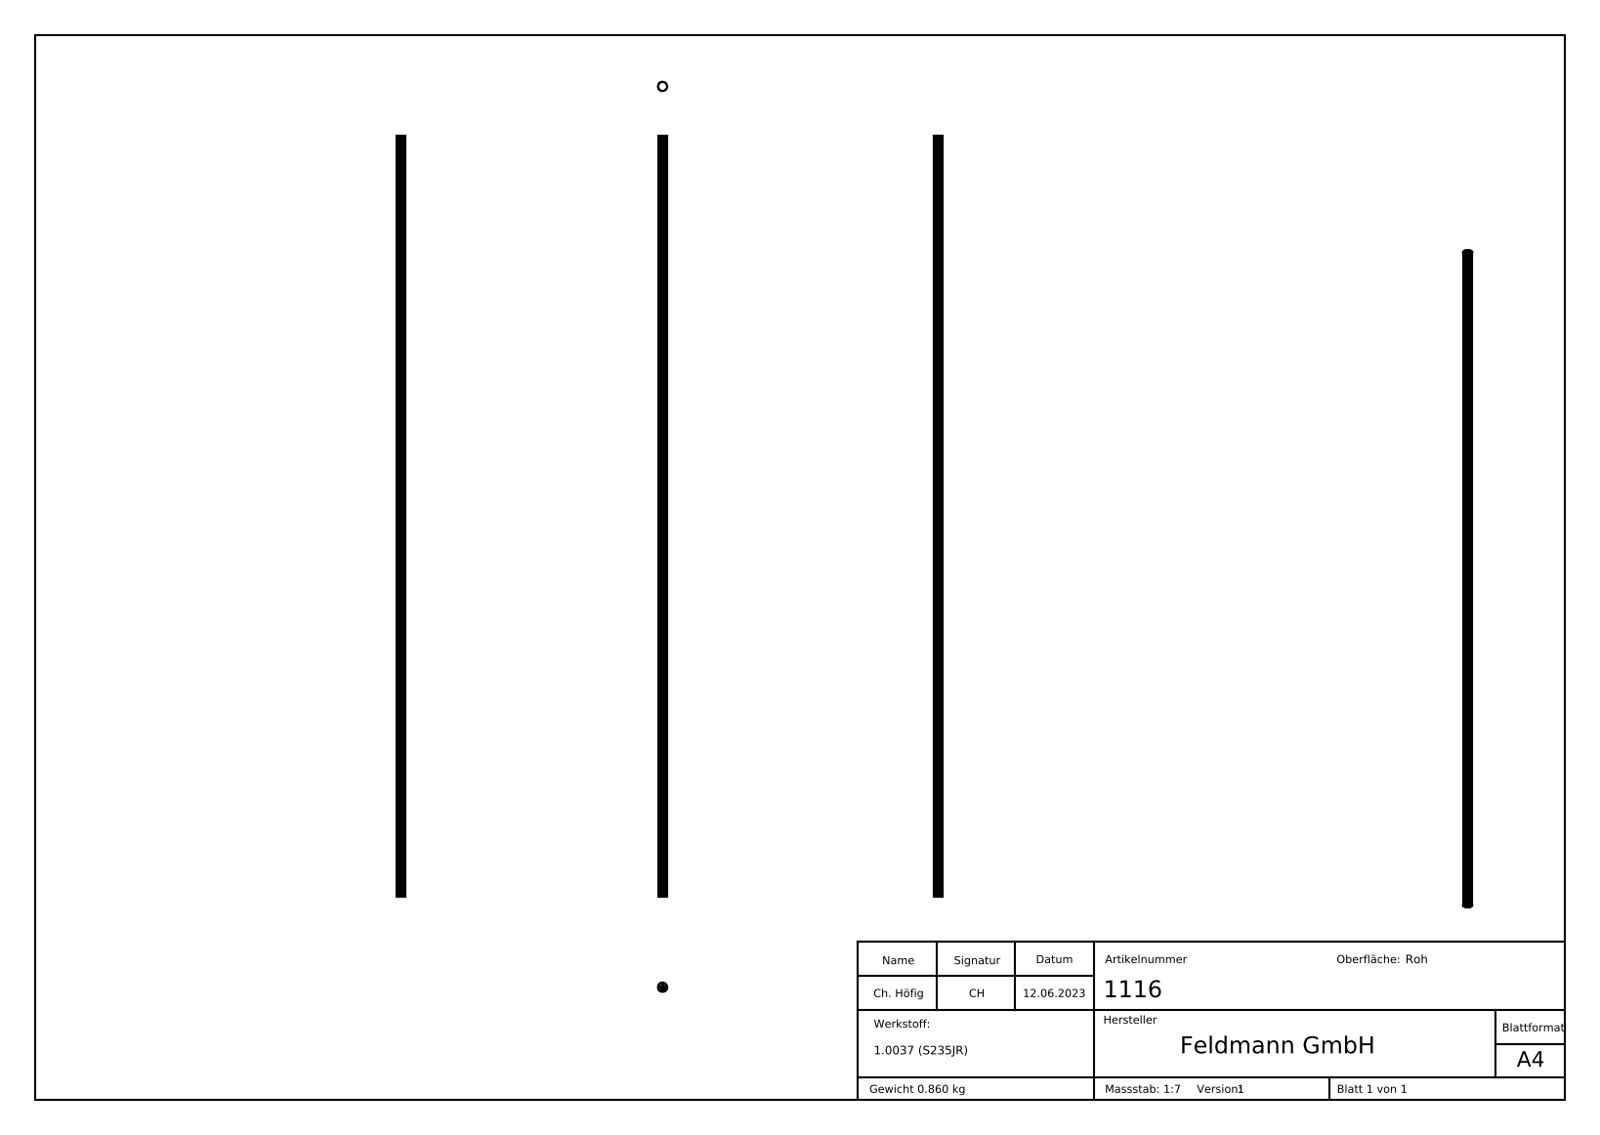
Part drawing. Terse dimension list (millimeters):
name: 1116
written by: SolidWorks 2018 (CONFIG_CONTROL_DESIGN)
unit: mm
bodies: 1 solid, 209 faces (132 planar, 0 cylindrical, 77 other)
size: 1000 × 11.77 × 11.77
volume: 110 212 mm³; area: 37 686 mm²
face distances: 11.76, 11.78, 1000, 999.9, 1.02, 1.26, 1.32, 0.36, 1.2, 1.35
